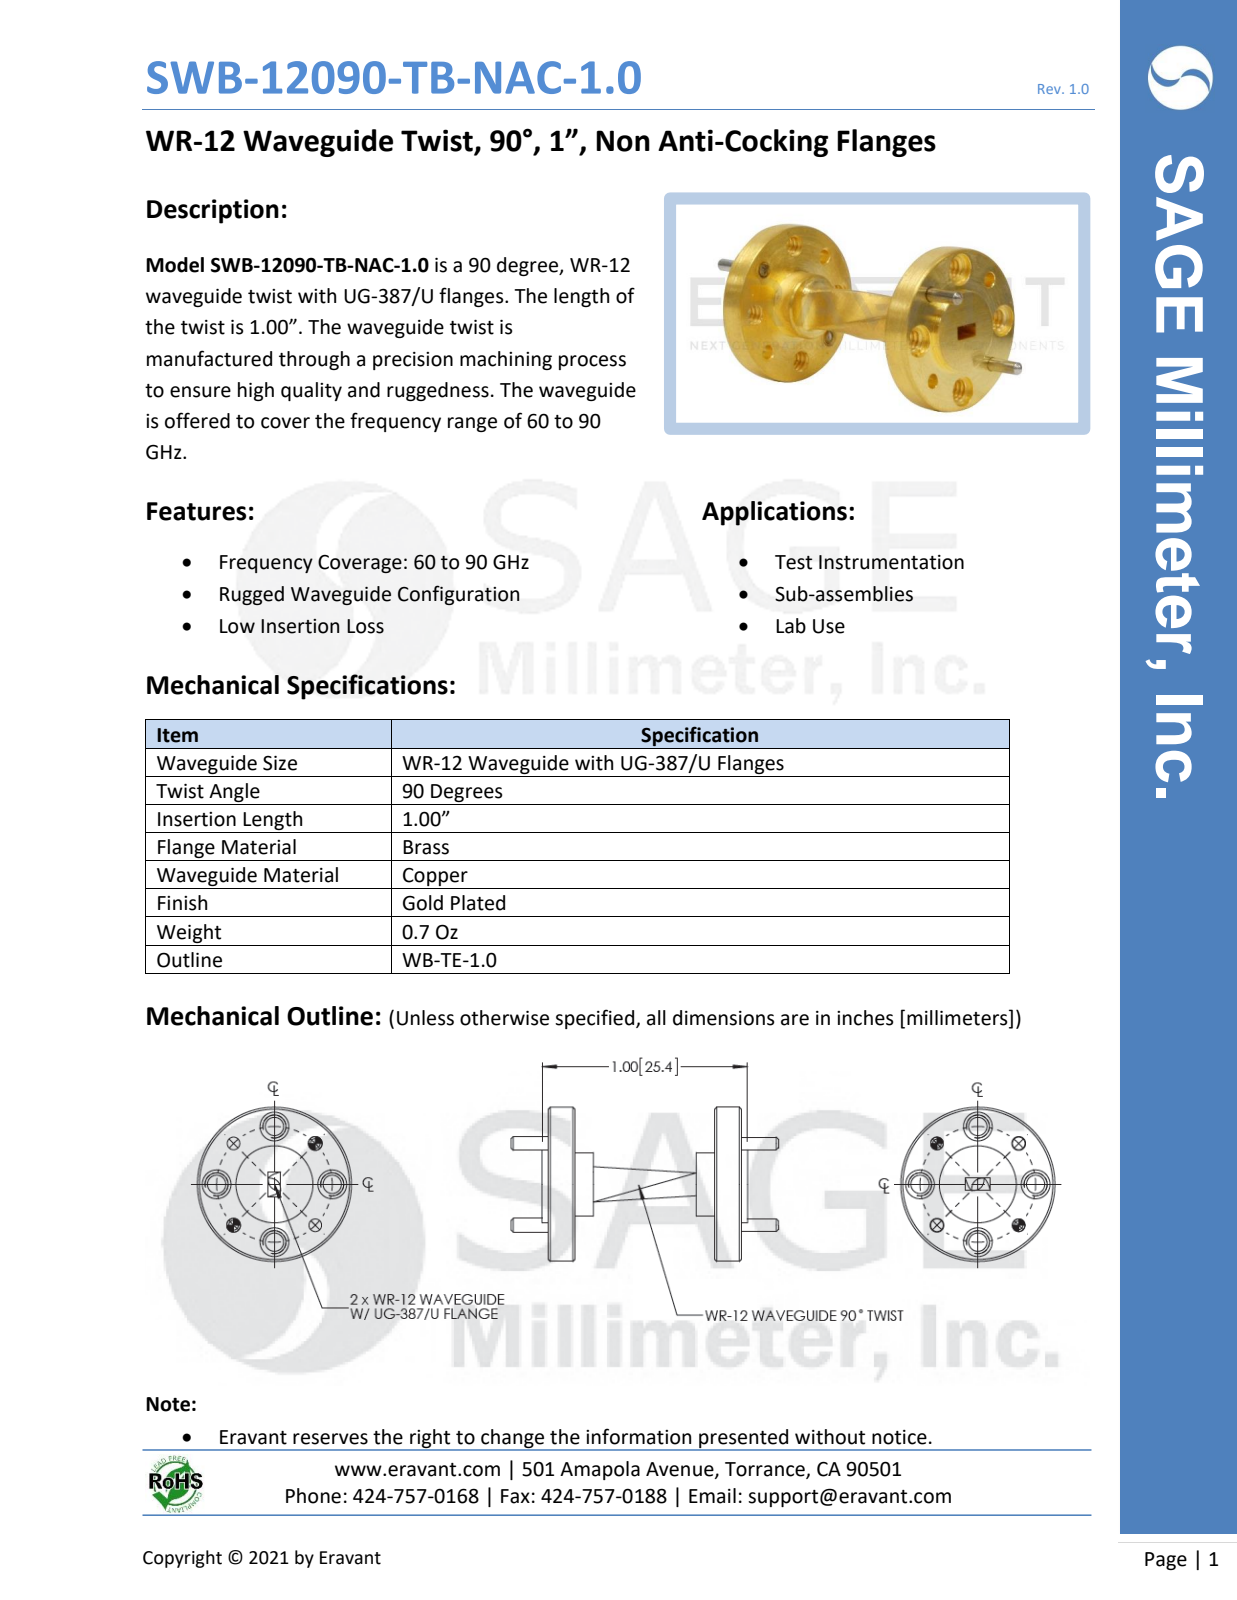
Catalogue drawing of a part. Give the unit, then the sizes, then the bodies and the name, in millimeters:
Units: millimetres
Overall size (bounding box): 33.1 × 19.1 × 19.1
Round holes (diameter × count): ⌀2.3 ×4, ⌀3.6 ×4, ⌀1.5 ×2, ⌀1.7 ×2
Round bosses / shafts (diameter × count): ⌀1.6 ×2, ⌀19.1 ×1, ⌀9.5 ×1, ⌀7.9 ×1
Main face-to-face distances: 3.3, 20.6, 17.3, 23.9, 0.8, 4.1, 21.3, 24.6, 6.4, 19.1
Hole centre spacings: 5.5, 10.1, 13.2, 14.3
Volume: 2 180 mm³ · Surface area: 2 192 mm²
Bodies: 5 solids, 146 faces (34 planar, 68 cylindrical, 44 other)
Part name (STEP PRODUCT): SWB-12090-TB-1.0
STEP written by: SolidWorks 2016 (AUTOMOTIVE_DESIGN)
